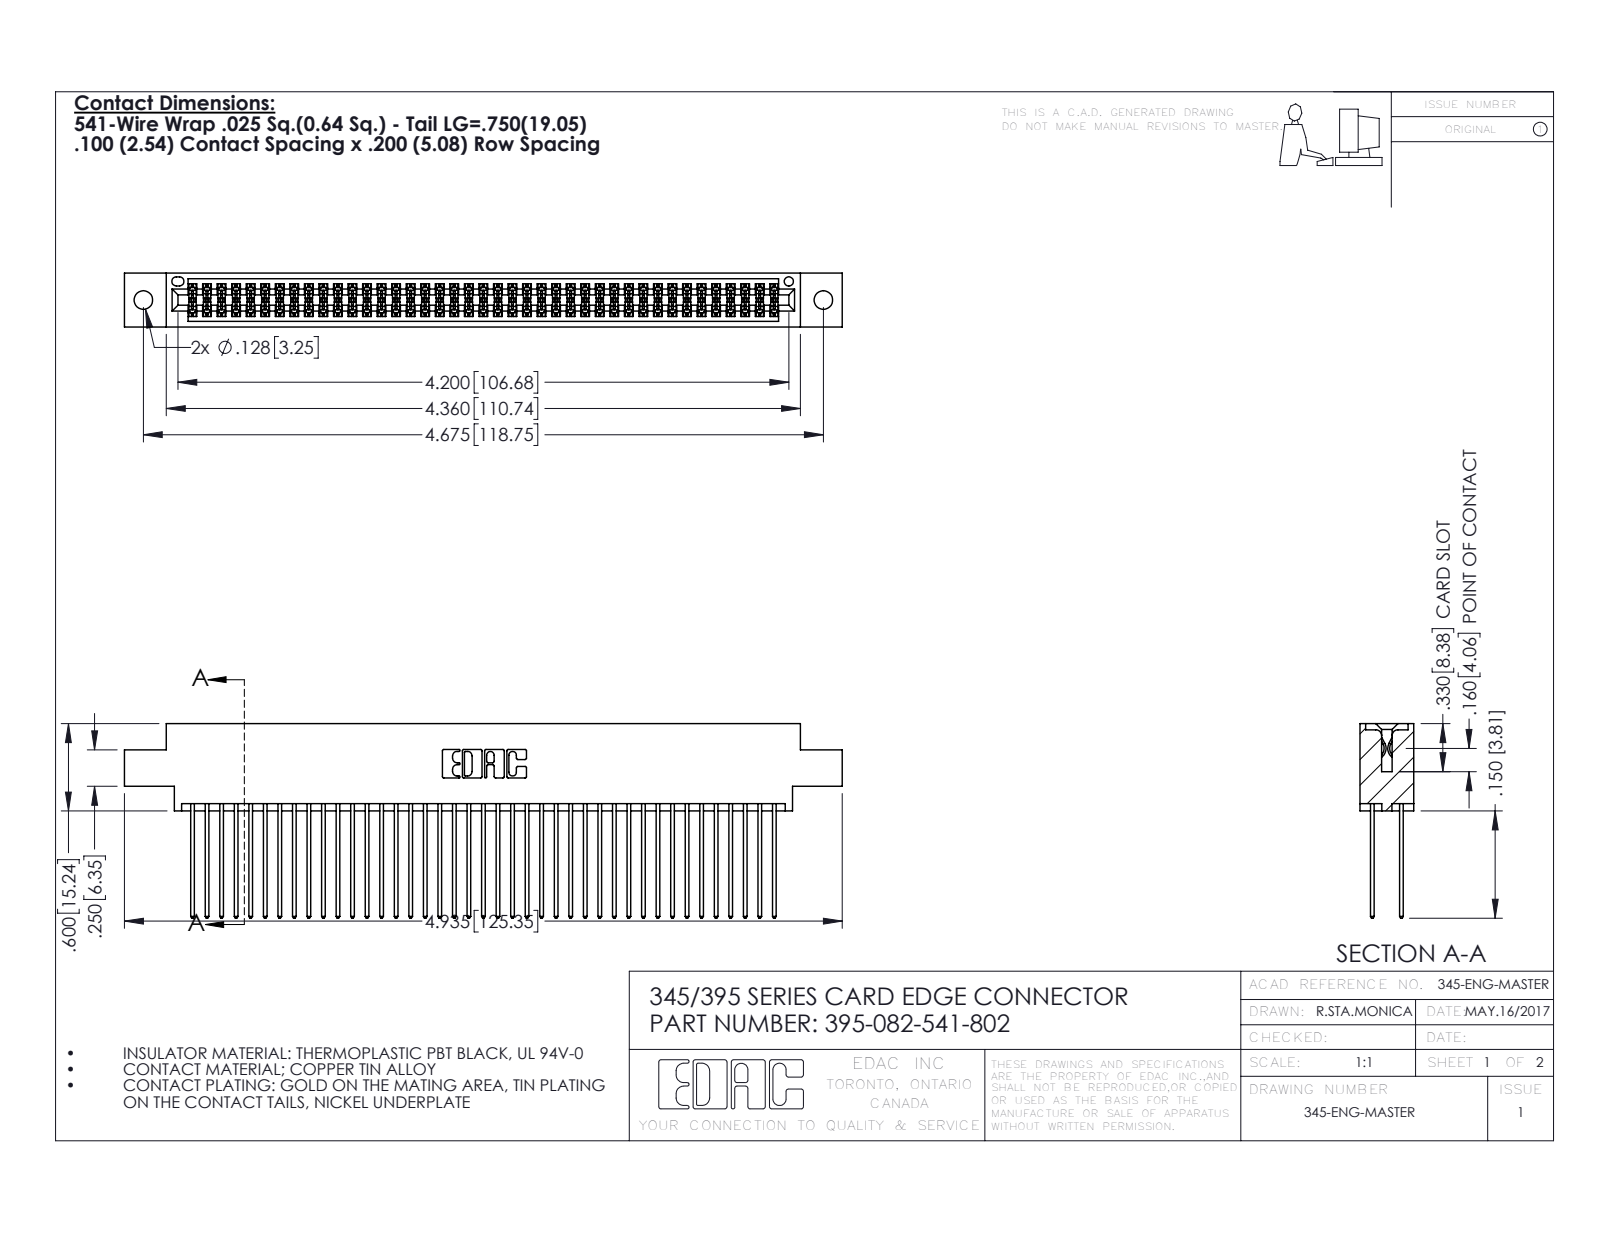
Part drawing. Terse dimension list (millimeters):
name: 395-082-541-802; 345-292-001_345-293-141; 345 Part_0.170 Offset - 0.128 Dia
written by: SolidWorks 2016 (CONFIG_CONTROL_DESIGN)
unit: mm
bodies: 83 solids, 4230 faces (2790 planar, 1440 cylindrical, 0 other)
size: 125.3 × 34 × 9.4
volume: 12 500 mm³; area: 20 520 mm²
holes: 2× ⌀3.3, 1× ⌀1.6
rounds: 123× R0.2, 82× R0.3, 22× R0.3, 6× R0.2, 6× R0.8, 3× R0.7, 2× R0.4, 2× R0.5
face distances: 7.6, 1.8, 5.1, 2.5, 6.9, 0.6, 9.4, 5.7, 4.4, 3.8
hole spacings: 6.9, 112.8, 118.7
